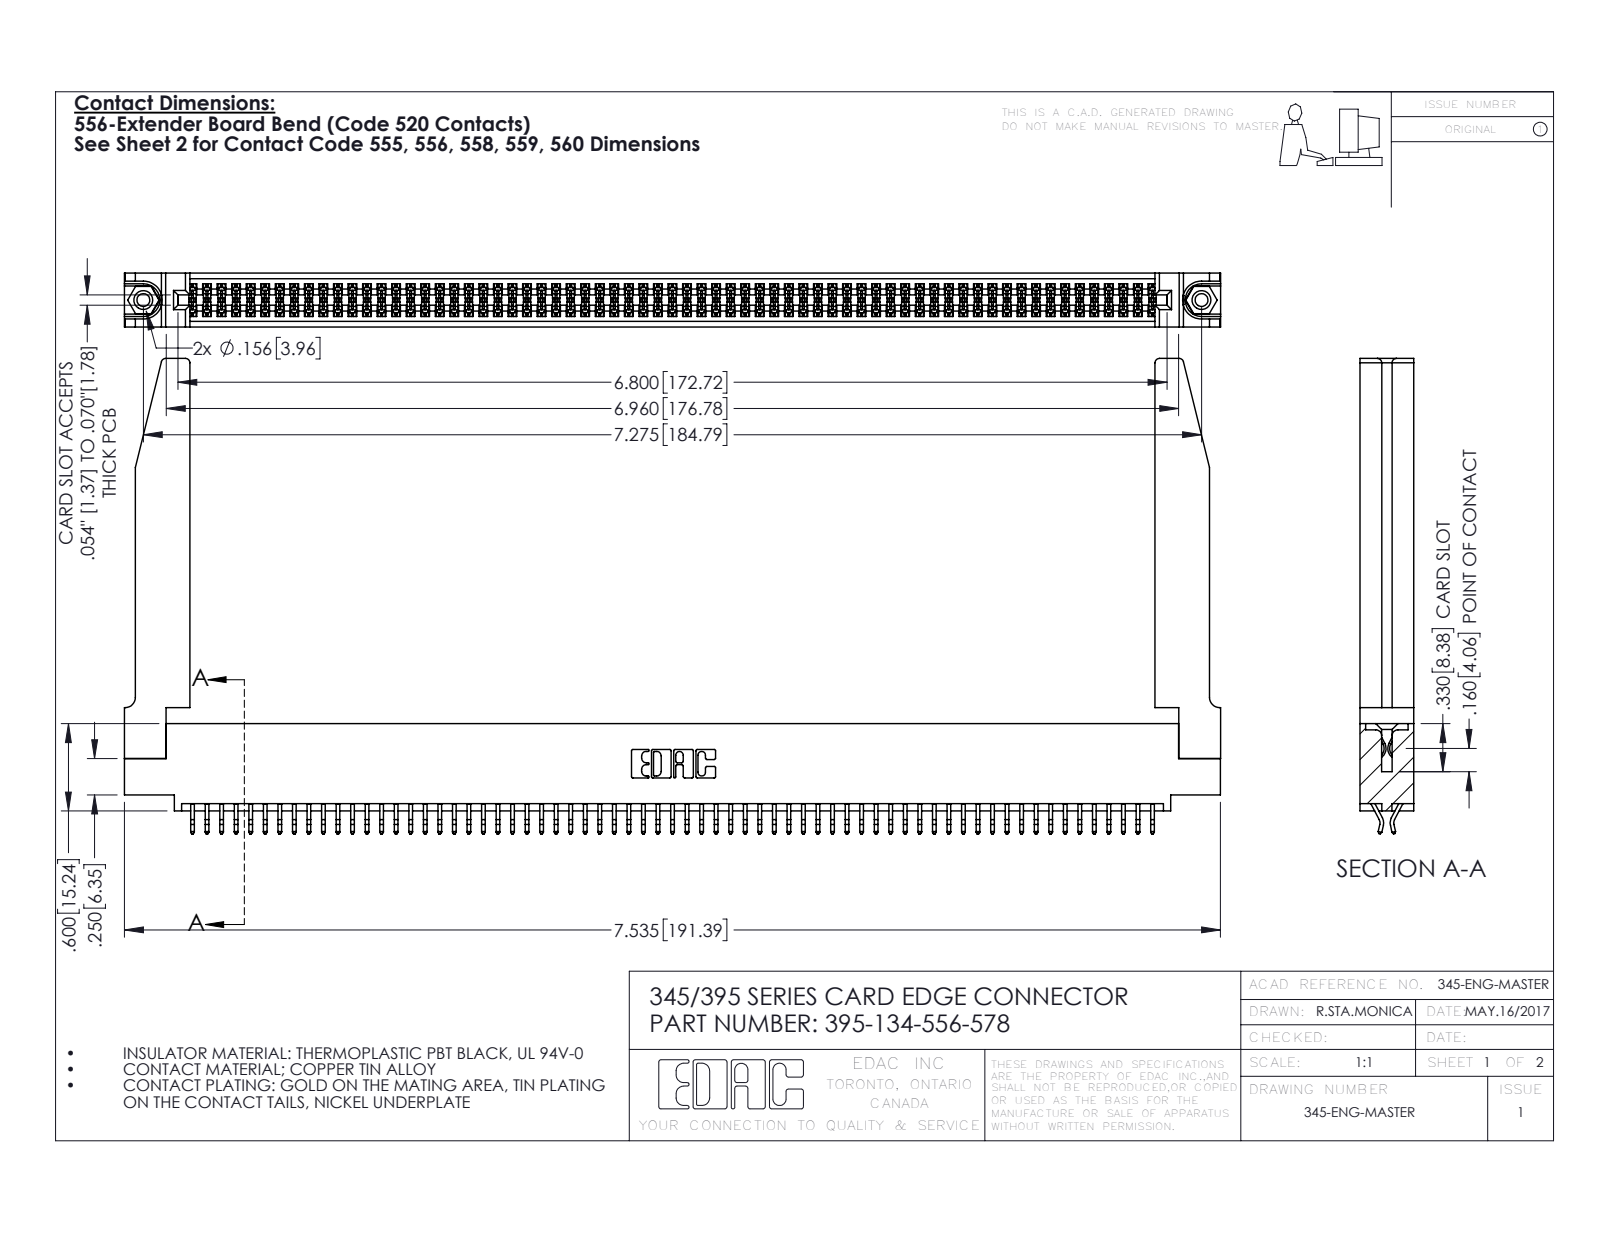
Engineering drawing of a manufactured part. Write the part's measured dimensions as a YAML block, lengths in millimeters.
part_name: "345 Part_0.110 Offset - 0.156 Dia-TH; 345-292-001_556 Tail; 395-134-556-578; 345-250-001_345-250-001-102 (+1 more)"
step_written_by: "SolidWorks 2016 (CONFIG_CONTROL_DESIGN)"
units: millimeters
bodies: {solids: 139, faces: 7868, planar: 5184, cylindrical: 2632, other: 52}
overall_size: [191.4, 83, 9.4]
volume: 26510
surface_area: 35010
round_holes:
  - {diameter: 2.3, count: 2}
  - {diameter: 3.2, count: 2}
  - {diameter: 4, count: 2}
  - {diameter: 1.6, count: 1}
round_bosses_or_shafts:
  - {diameter: 3.9, count: 2}
partial_cylinders:
  - {radius: 0.2, count: 201}
  - {radius: 0.3, count: 22}
  - {radius: 0.8, count: 8}
  - {radius: 0.2, count: 6}
  - {radius: 0.8, count: 6}
  - {radius: 0.7, count: 3}
  - {radius: 0.3, count: 2}
  - {radius: 0.4, count: 2}
face_to_face_distances: [1.8, 7.6, 9.4, 0.6, 2.5, 6.9, 5.1, 5.7, 4.4, 3.8]
hole_center_spacings: [6.9, 178.8, 184.8]
